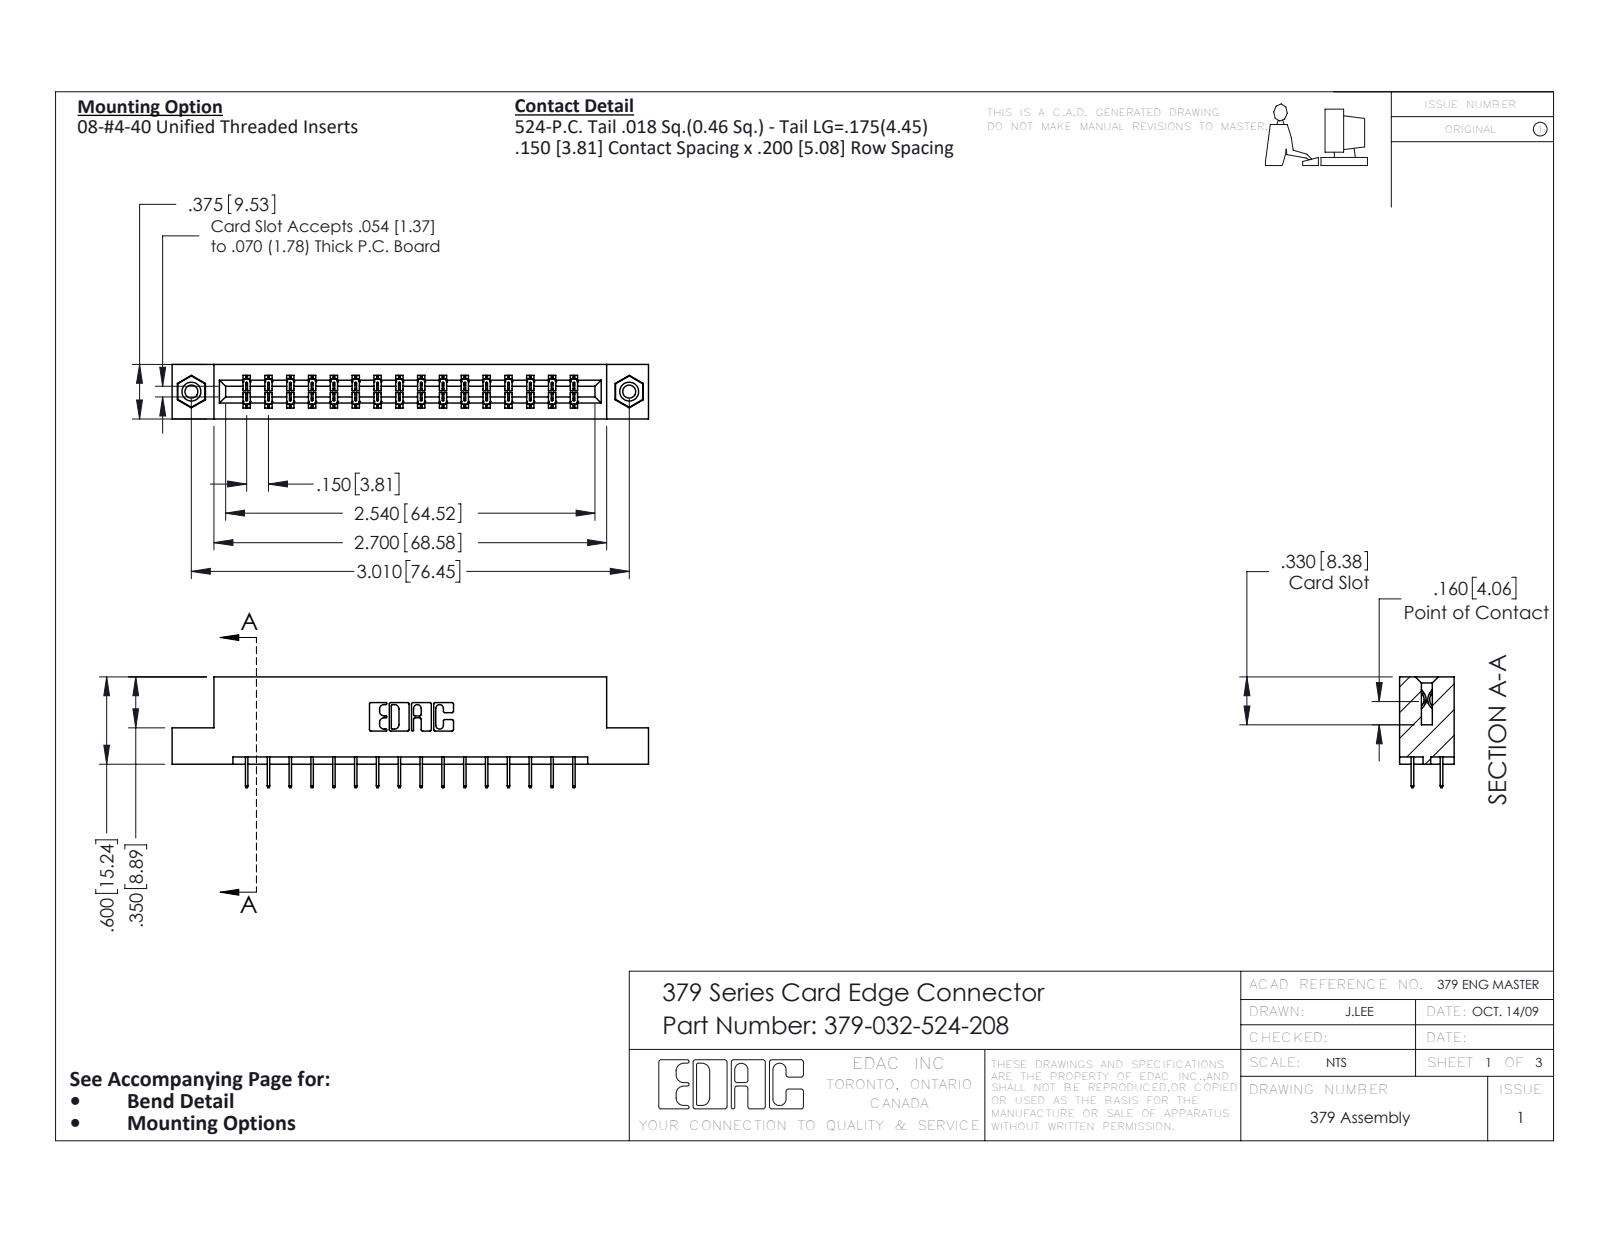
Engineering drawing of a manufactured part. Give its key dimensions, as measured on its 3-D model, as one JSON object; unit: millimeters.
{"part_name": "379 Part_Flush - .156 Dia - TI; 379-032-524-208; 345-292-001_345-293-124; 345-250-001_345-250-003-102", "step_written_by": "SolidWorks 2020 (CONFIG_CONTROL_DESIGN)", "units": "millimeters", "bodies": {"solids": 35, "faces": 1966, "planar": 1446, "cylindrical": 504, "other": 16}, "overall_size": [83.2, 19.4, 9.5], "volume_mm3": 8470, "surface_area_mm2": 9161, "round_holes": [[2.3, 2], [3.2, 2], [4, 2]], "round_bosses_or_shafts": [[3.9, 2]], "partial_cylinders_radius": [[0.2, 63], [0.3, 22], [0.2, 6], [0.8, 6], [0.7, 3], [0.4, 2], [0.6, 2], [0.6, 2]], "face_to_face_distances": [7.6, 9.5, 1.9, 5.1, 2.5, 3.8, 1.3, 15.2, 5.7, 14], "hole_center_spacings": [76.5]}
